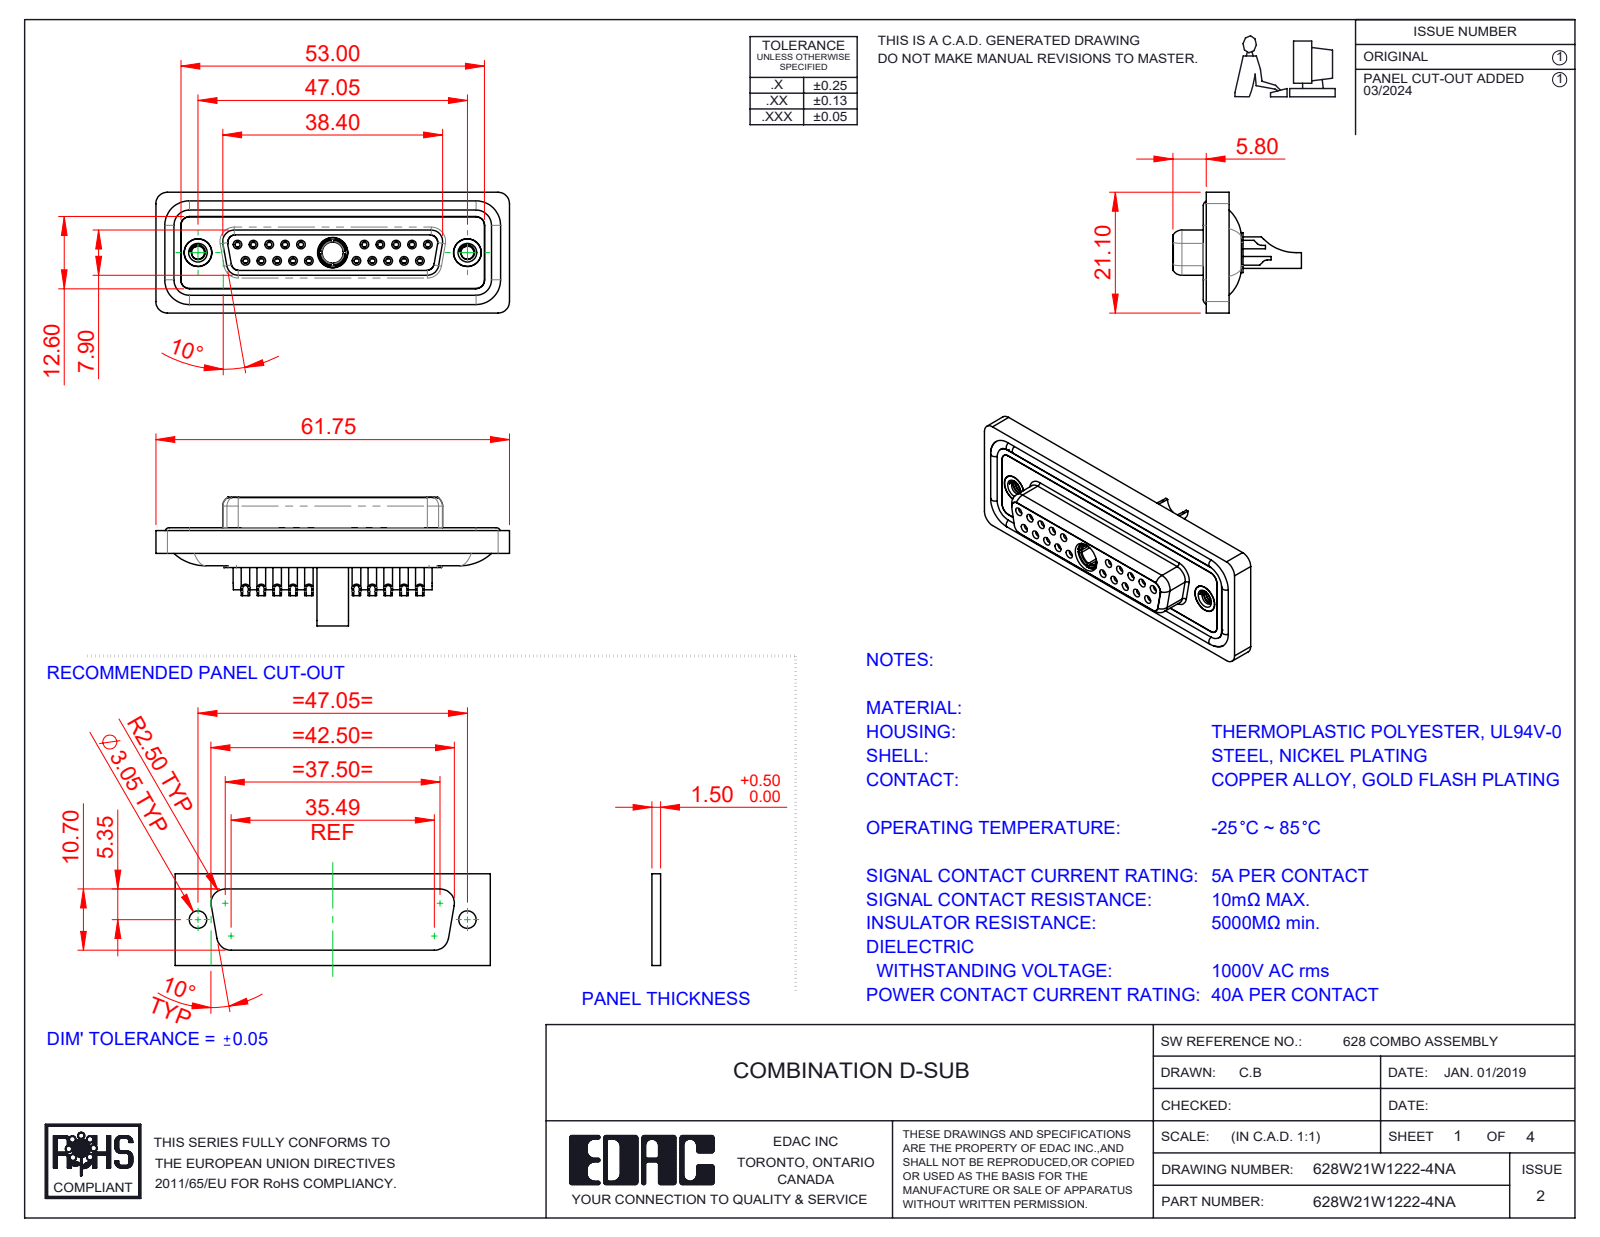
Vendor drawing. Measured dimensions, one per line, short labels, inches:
name: 628Combo Shell Front_25 Contacts; 628Combo Threaded Rivet_A; 628Combo Waterproof Housing_25 Contacts; 628Combo Shell Rear_25 Contacts (+5 more)
written by: SolidWorks 2023 (CONFIG_CONTROL_DESIGN)
unit: in
bodies: 29 solids, 1561 faces (476 planar, 634 cylindrical, 451 other)
size: 2.431 × 0.884 × 0.831
volume: 0.516 in³; area: 22.24 in²
holes: 20× ⌀0.035, 20× ⌀0.039, 20× ⌀0.043, 20× ⌀0.059, 20× ⌀0.079, 10× ⌀0.063, 10× ⌀0.067, 3× ⌀0.191, 2× ⌀0.089, 2× ⌀0.157, 2× ⌀0.159, 2× ⌀0.197
bosses: 20× ⌀0.087, 14× ⌀0.063, 2× ⌀0.195, 2× ⌀0.189, 1× ⌀0.217, 1× ⌀0.205, 1× ⌀0.195, 1× ⌀0.187
rounds: 22× R0.059, 18× R0.079, 8× R0.053, 8× R0.063, 6× R0.039, 4× R0.01, 4× R0.02, 4× R0.024
face distances: 0.016, 0.071, 0.293, 0.222, 0.26, 0.02, 0.063, 0.278, 0.114, 0.043
hole spacings: 0.124, 0.109, 0.218, 0.198, 0.327, 0.294, 0.654, 0.763
